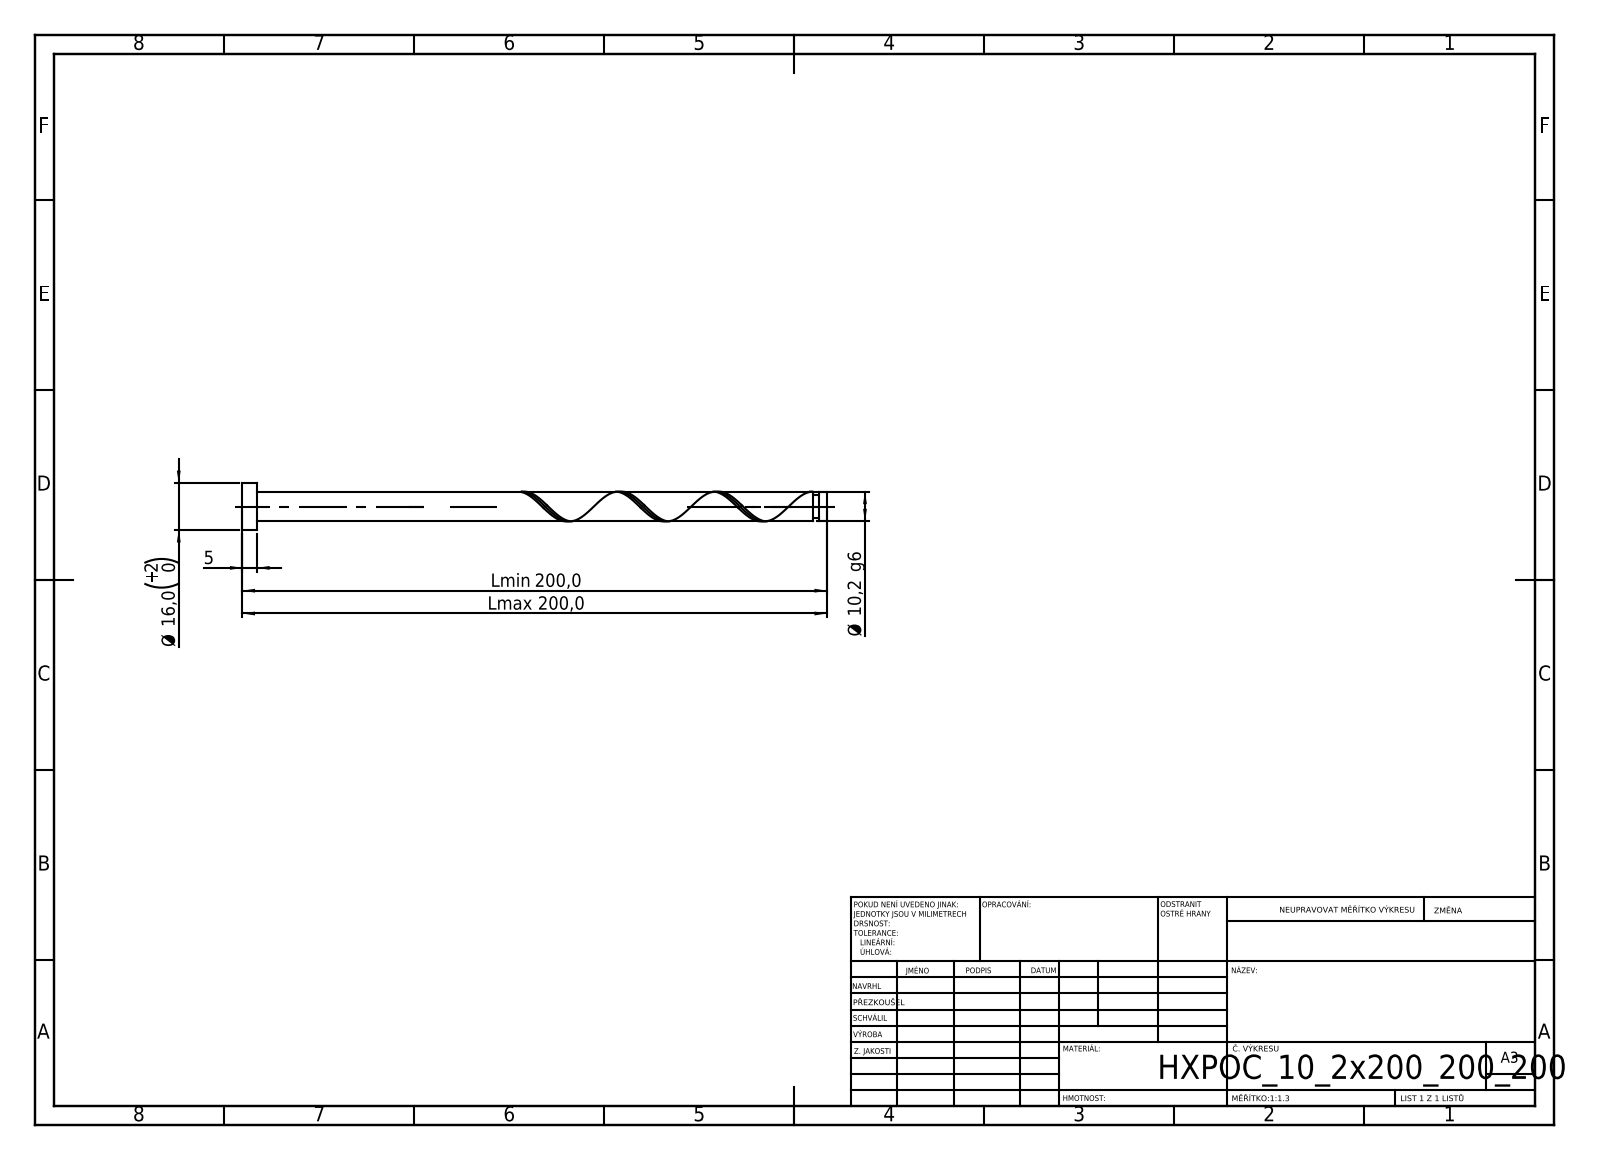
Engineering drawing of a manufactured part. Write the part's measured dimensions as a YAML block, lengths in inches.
step_written_by: "SolidWorks 2019 (CONFIG_CONTROL_DESIGN)"
units: inches
bodies: {solids: 1, faces: 21, planar: 6, cylindrical: 14, other: 1}
overall_size: [7.874, 0.63, 0.63]
volume: 1.021
surface_area: 11.01
round_bosses_or_shafts:
  - {diameter: 0.63, count: 1}
  - {diameter: 0.402, count: 1}
  - {diameter: 0.321, count: 1}
face_to_face_distances: [0.197, 7.874, 7.677, 7.766, 7.569, 0.108, 7.686, 7.489, 0.08, 0.188]
